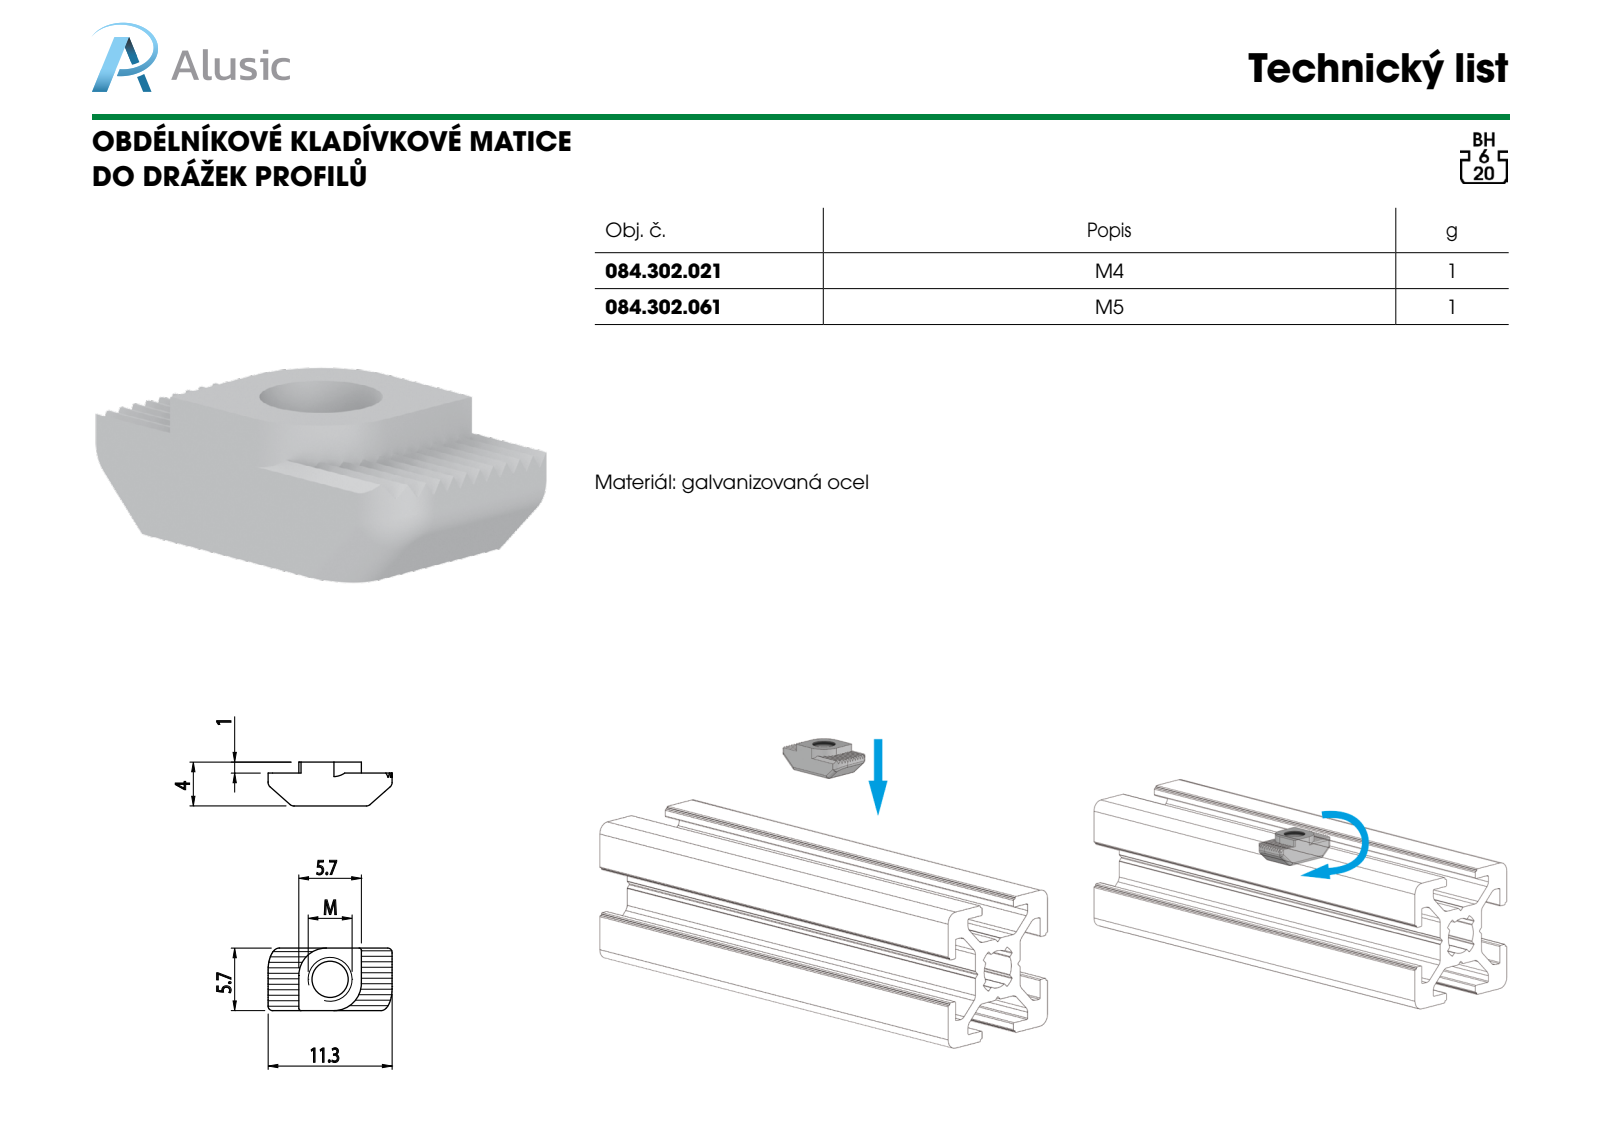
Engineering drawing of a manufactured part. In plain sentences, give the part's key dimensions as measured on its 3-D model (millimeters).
The part is named "084.302.061". Its 3-D file was written by "SolidWorks 2012 (CONFIG_CONTROL_DESIGN)". It is 1 solid with 70 faces: 58 planar, 10 cylindrical and 2 other. Overall it measures 11.3 by 5.7 by 4 millimeters. Its volume is 141 cubic millimeters and its surface area 280 square millimeters. Round holes: 1 of diameter 4.2. Partial cylindrical surfaces (rounded edges, fillets, slot ends): 2 of radius 1, 2 of radius 1.1, 2 of radius 1.5, 2 of radius 2.5. The main face-to-face distances are 5.7, 0.85, 0.42, 2.12, 1.27, 1.7, 0.43, 1.95, 4, 2.54.
